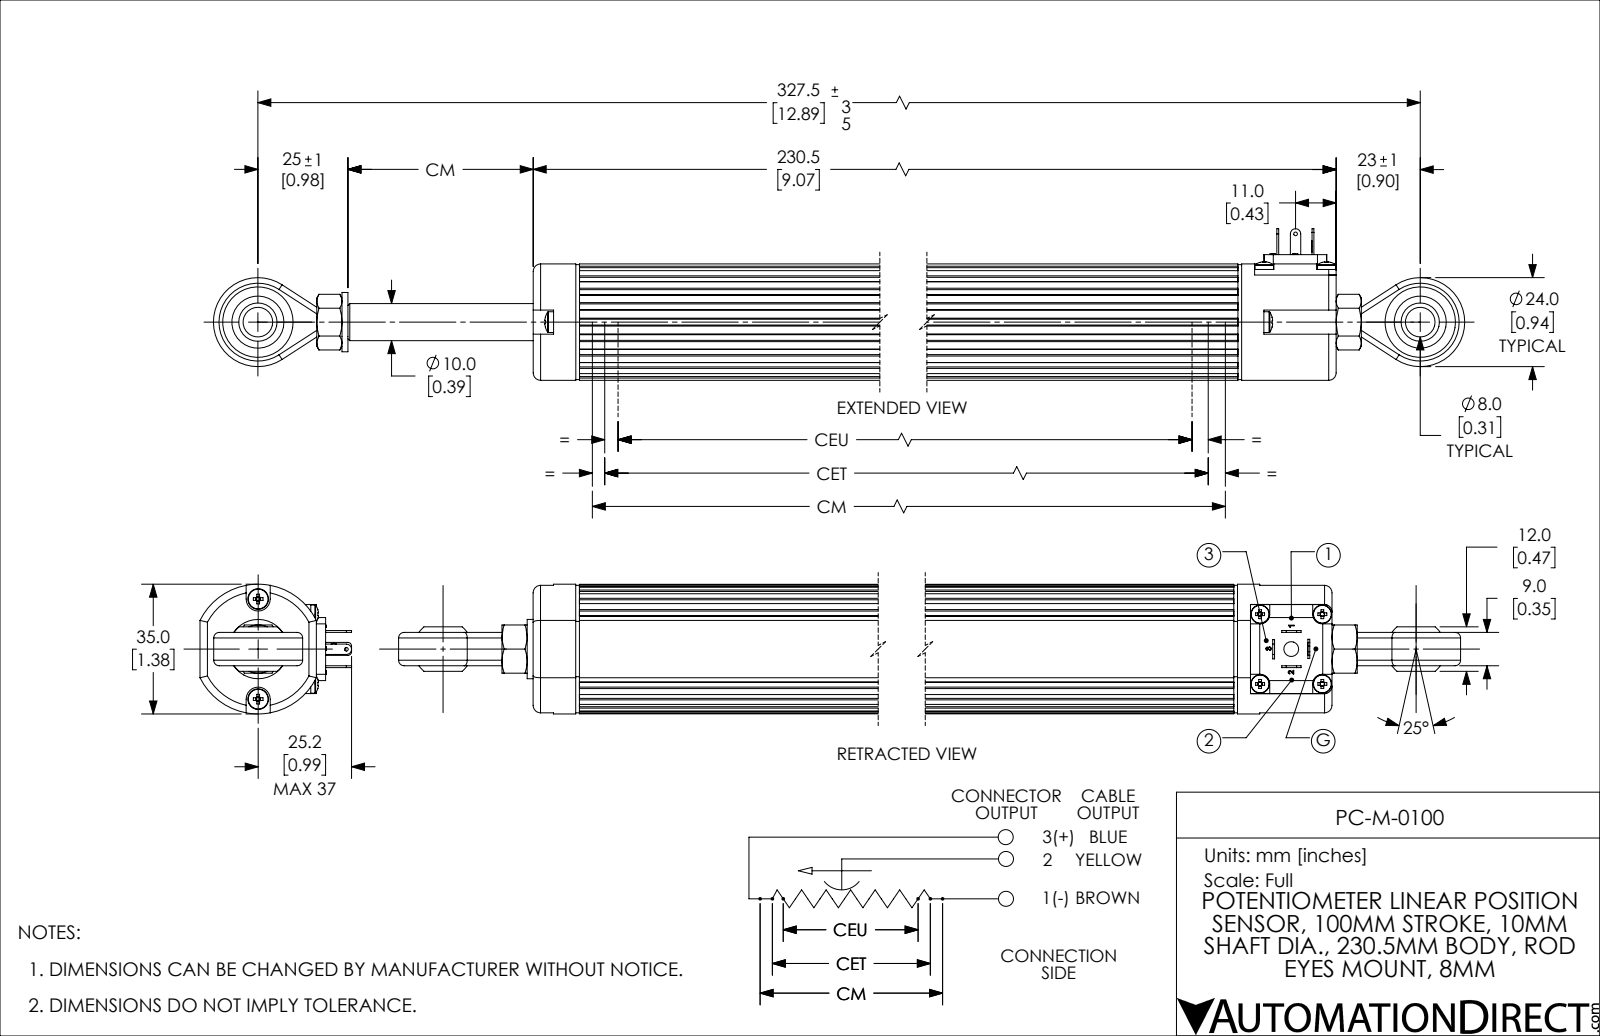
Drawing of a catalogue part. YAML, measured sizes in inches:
part_name: "PC-M-0100"
step_written_by: "SolidWorks 2019 (AUTOMOTIVE_DESIGN)"
units: inches
bodies: {solids: 26, faces: 1447, planar: 437, cylindrical: 366, other: 644}
overall_size: [11.87, 1.61, 1.378]
volume: 14.07
surface_area: 88.67
round_holes:
  - {diameter: 0.087, count: 4}
  - {diameter: 0.102, count: 4}
  - {diameter: 0.039, count: 3}
  - {diameter: 0.108, count: 2}
  - {diameter: 0.138, count: 2}
  - {diameter: 0.315, count: 2}
  - {diameter: 0.748, count: 2}
  - {diameter: 0.114, count: 1}
  - {diameter: 0.157, count: 1}
  - {diameter: 0.268, count: 1}
  - {diameter: 0.331, count: 1}
  - {diameter: 0.512, count: 1}
round_bosses_or_shafts:
  - {diameter: 0.197, count: 4}
  - {diameter: 0.098, count: 4}
  - {diameter: 0.118, count: 3}
  - {diameter: 0.22, count: 2}
  - {diameter: 0.63, count: 1}
  - {diameter: 0.394, count: 1}
  - {diameter: 0.39, count: 1}
  - {diameter: 0.315, count: 1}
partial_cylinders:
  - {radius: 0.059, count: 8}
  - {radius: 0.039, count: 5}
  - {radius: 0.079, count: 5}
  - {radius: 0.102, count: 4}
  - {radius: 0.118, count: 4}
  - {radius: 0.055, count: 2}
  - {radius: 0.128, count: 2}
  - {radius: 0.472, count: 2}
face_to_face_distances: [1.236, 0.039, 7.579, 7.539, 7.618, 0.118, 1.118, 0.492, 0.453, 8.622]
hole_center_spacings: [0.496, 0.531, 0.661, 0.74, 0.993, 0.024, 0.11, 0.134]
